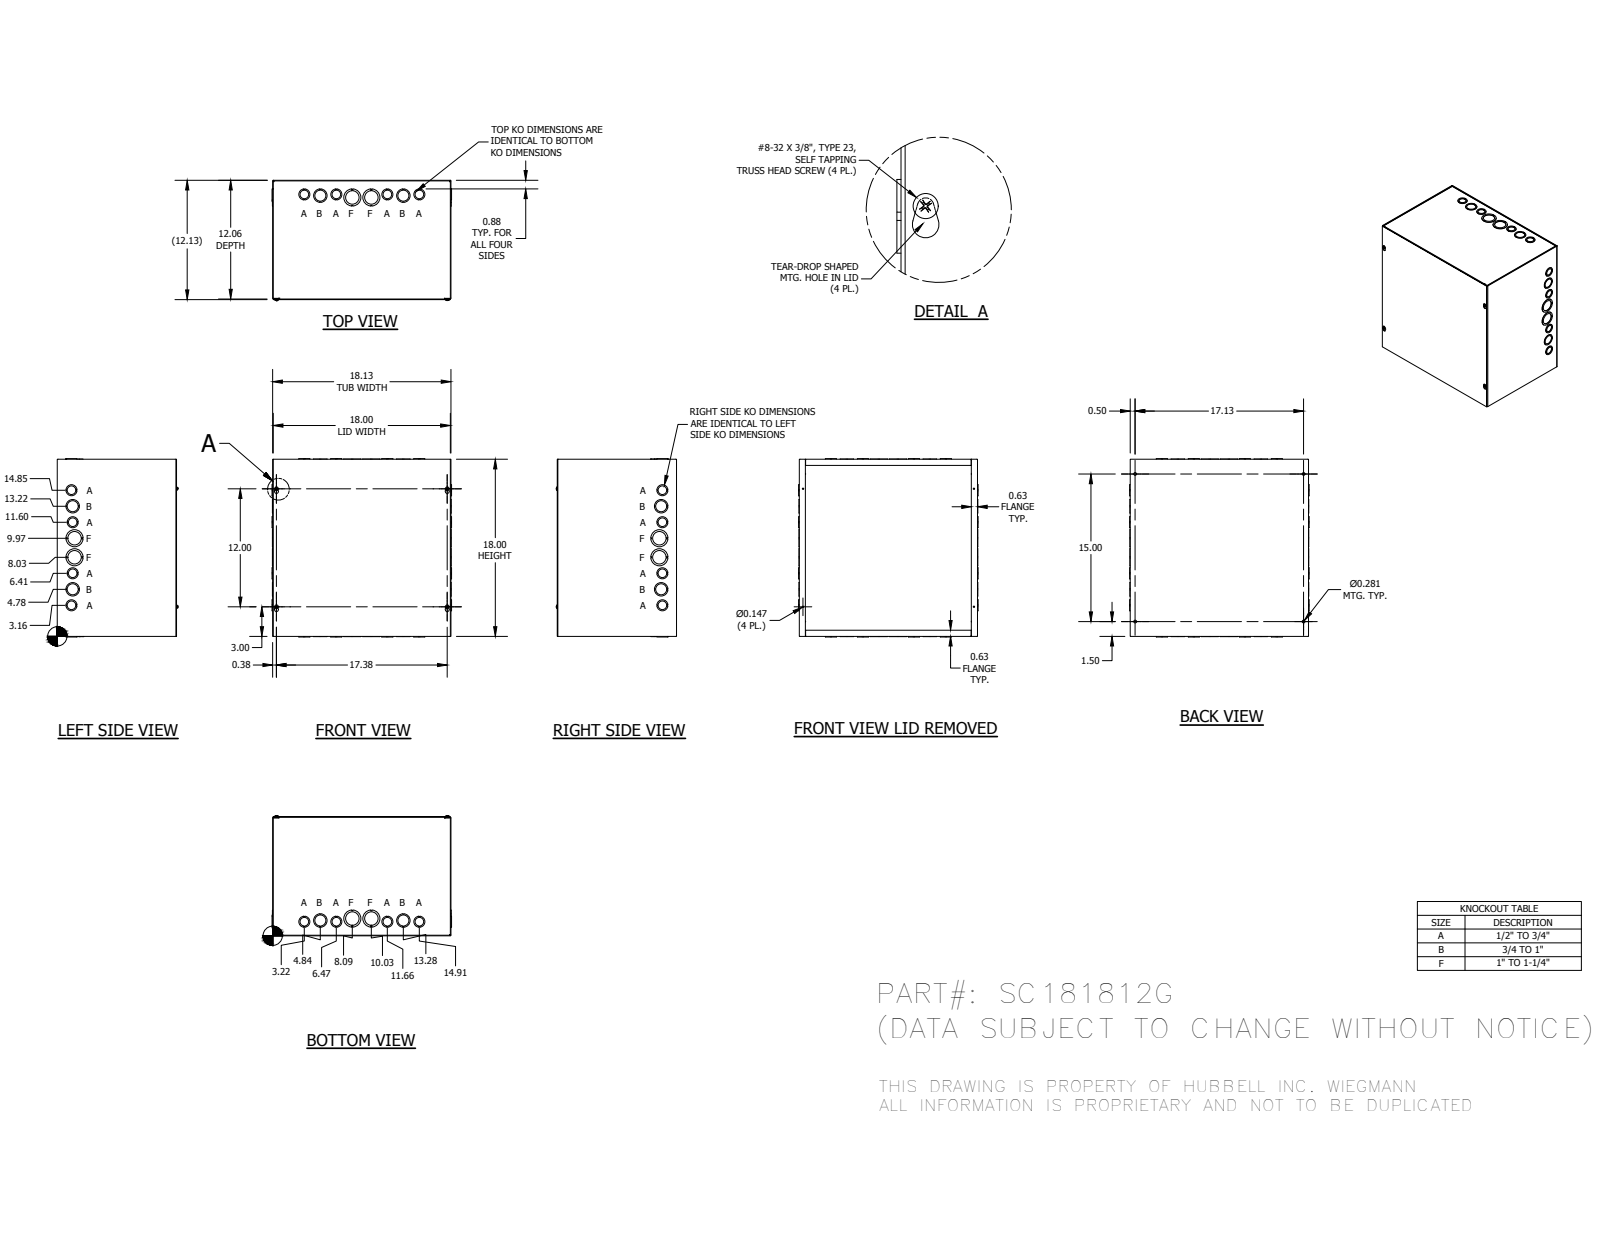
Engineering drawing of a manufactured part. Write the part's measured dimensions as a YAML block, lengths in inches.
part_name: "SC181812GBLR; SC1812GTB; SC1818GLPA; 34056 (+1 more)"
step_written_by: "Autodesk Inventor 2014 (AUTOMOTIVE_DESIGN)"
units: inches
bodies: {solids: 37, faces: 1167, planar: 859, cylindrical: 240, other: 68}
overall_size: [18.25, 18.125, 12.225]
round_holes:
  - {diameter: 1.125, count: 14}
  - {diameter: 0.875, count: 10}
  - {diameter: 1.375, count: 8}
  - {diameter: 0.147, count: 4}
  - {diameter: 0.281, count: 4}
  - {diameter: 1.75, count: 4}
round_bosses_or_shafts:
  - {diameter: 0.384, count: 4}
  - {diameter: 0.164, count: 4}
partial_cylinders:
  - {radius: 0.016, count: 12}
  - {radius: 0.078, count: 12}
  - {radius: 0.125, count: 4}
  - {radius: 0.203, count: 4}
face_to_face_distances: [0.063, 18, 17.937, 18.063, 12, 0.062, 12.062, 12.063, 12.125, 17.875]
hole_center_spacings: [1.505, 1.63, 1.63, 1.655, 3.25, 3.256, 3.579, 4.885]
